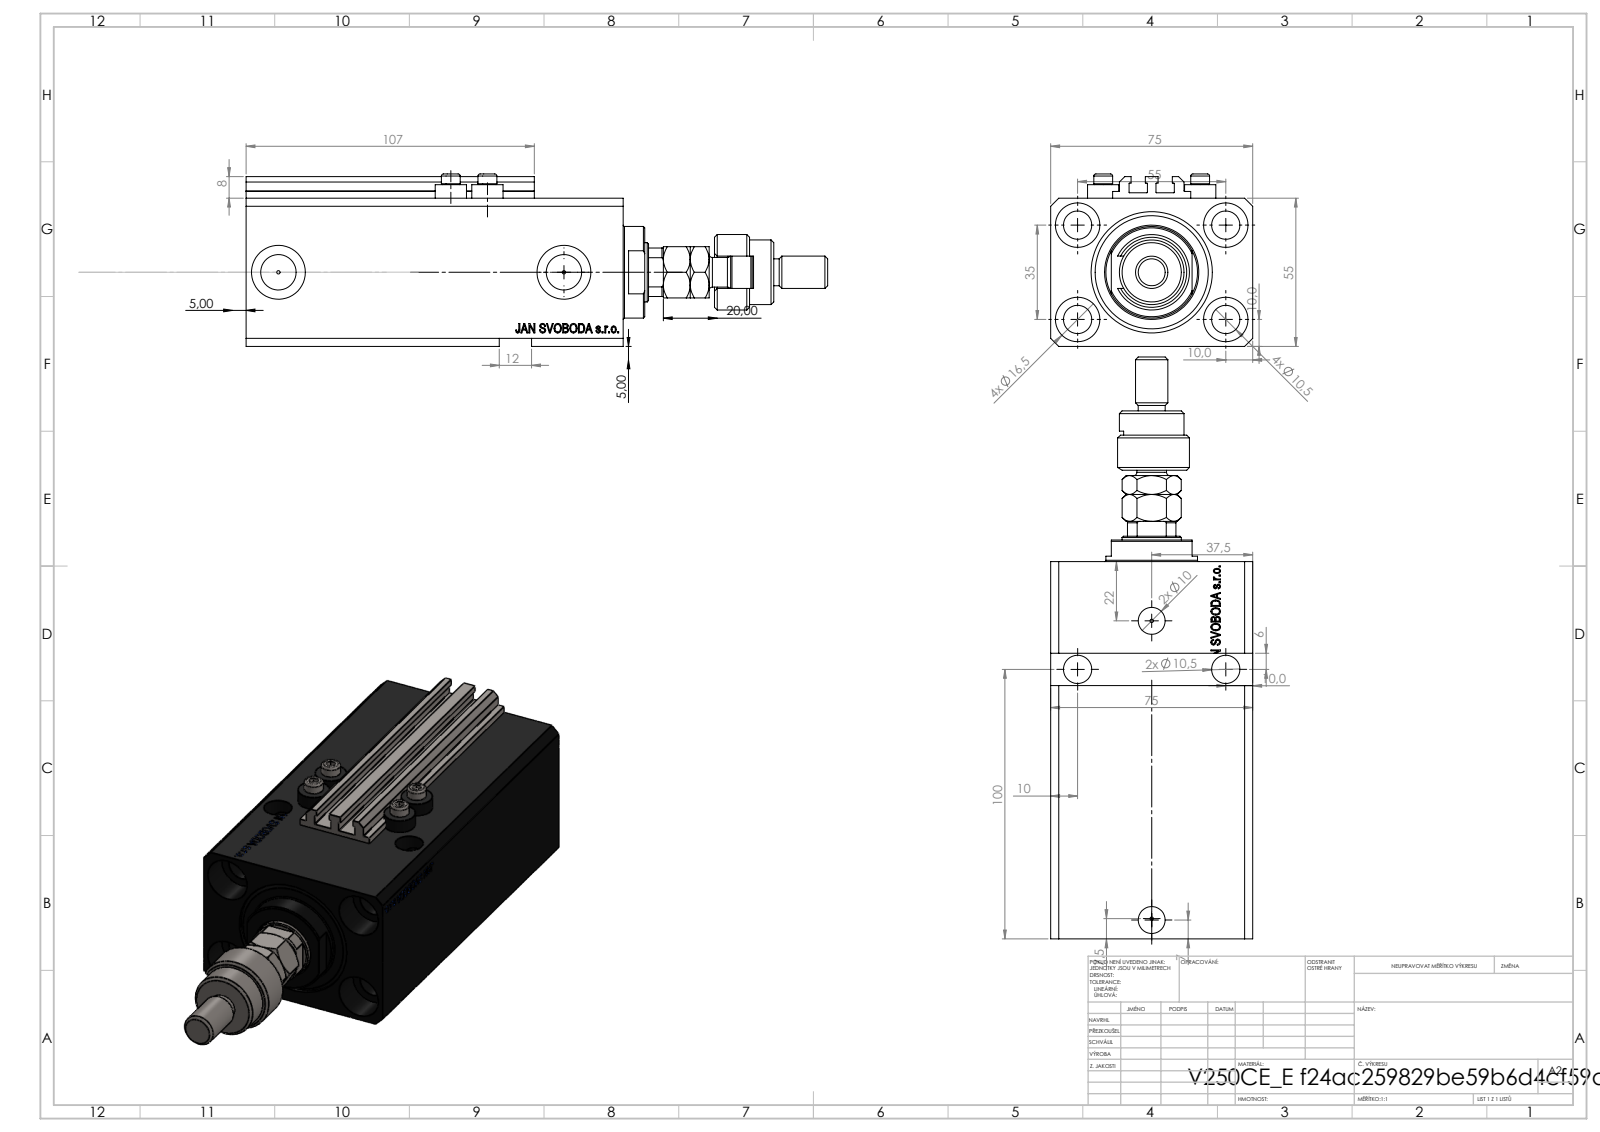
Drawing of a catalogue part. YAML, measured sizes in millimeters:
part_name: "FEMALE_PART_FOR_DFA; V250CE_C_VCP; V250CE_E_Body; ALLEN BOLT V250CE (+2 more)"
step_written_by: "SolidWorks 2019 (CONFIG_CONTROL_DESIGN)"
units: millimeters
bodies: {solids: 10, faces: 1169, planar: 542, cylindrical: 159, other: 468}
overall_size: [216, 75, 64]
volume: 503099
surface_area: 122425
round_holes:
  - {diameter: 10.5, count: 9}
  - {diameter: 1.25, count: 4}
  - {diameter: 4, count: 4}
  - {diameter: 16.5, count: 4}
  - {diameter: 10, count: 2}
  - {diameter: 13.16, count: 2}
  - {diameter: 20, count: 2}
  - {diameter: 22, count: 1}
  - {diameter: 32, count: 1}
  - {diameter: 45, count: 1}
round_bosses_or_shafts:
  - {diameter: 11.6, count: 4}
  - {diameter: 7, count: 4}
  - {diameter: 34, count: 1}
  - {diameter: 28, count: 1}
  - {diameter: 24, count: 1}
  - {diameter: 18, count: 1}
  - {diameter: 12, count: 1}
  - {diameter: 11, count: 1}
partial_cylinders:
  - {radius: 0.2, count: 10}
  - {radius: 9.75, count: 1}
  - {radius: 10.5, count: 1}
face_to_face_distances: [55, 75, 15, 140, 3, 8, 125, 9.9, 57, 115.1]
hole_center_spacings: [32.6, 32.87, 55, 96.98, 13.6, 14.09, 25.81, 32.58]
